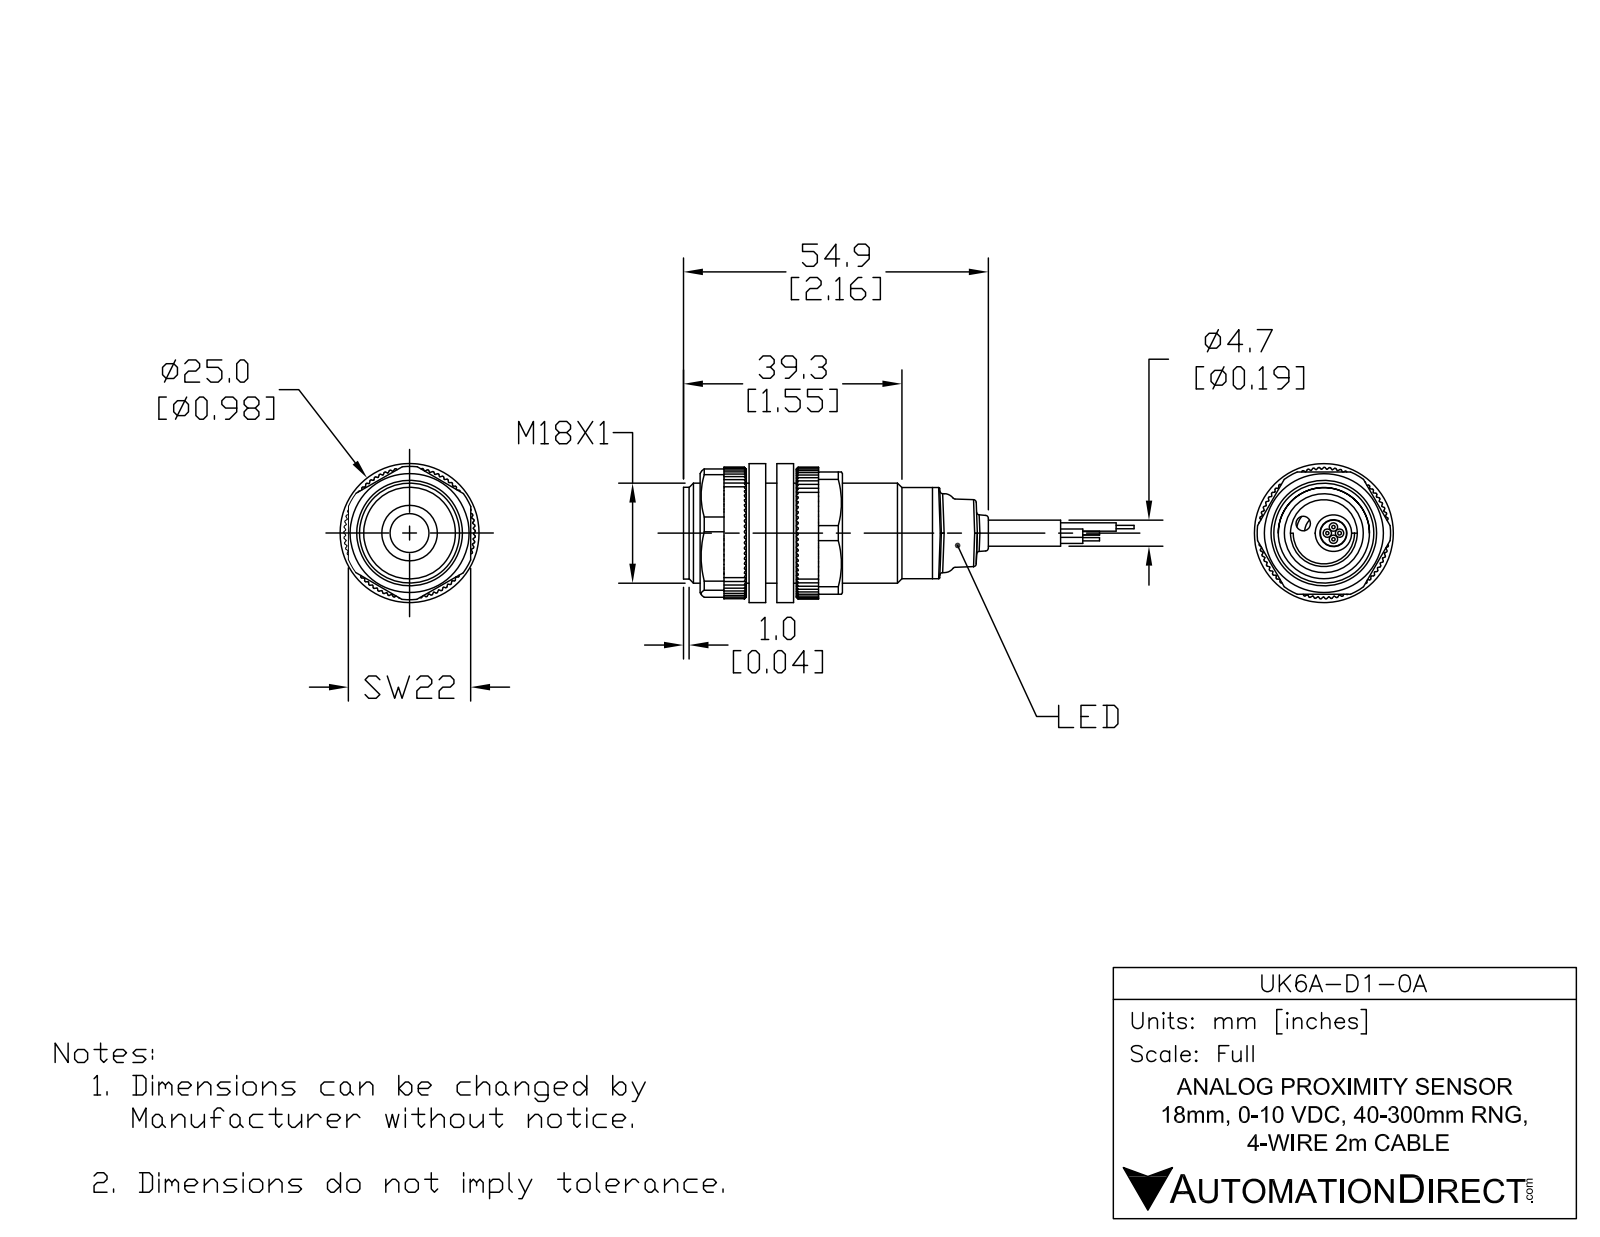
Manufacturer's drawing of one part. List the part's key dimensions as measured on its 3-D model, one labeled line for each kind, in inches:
Part name (STEP PRODUCT): UK6A-D1-0A
STEP written by: SolidWorks 2017 (AUTOMOTIVE_DESIGN)
Units: inches
Bodies: 4 solids, 62 faces (14 planar, 19 cylindrical, 29 other)
Overall size (bounding box): 3.537 × 0.709 × 0.709
Volume: 0.787 in³ · Surface area: 7.432 in²
Round holes (diameter × count): ⌀0.185 ×1, ⌀0.374 ×1
Round bosses / shafts (diameter × count): ⌀0.709 ×1, ⌀0.646 ×1, ⌀0.622 ×1, ⌀0.559 ×1
Partial cylindrical surfaces — rounded edges, fillets, slot ends (radius × count): R0.008 ×1, R0.02 ×1
Main face-to-face distances: 1.724, 0.039, 1.764, 0.039, 1.763, 1.963, 1.962, 1.923, 0.199, 0.255
Hole centre spacings: 0.068
